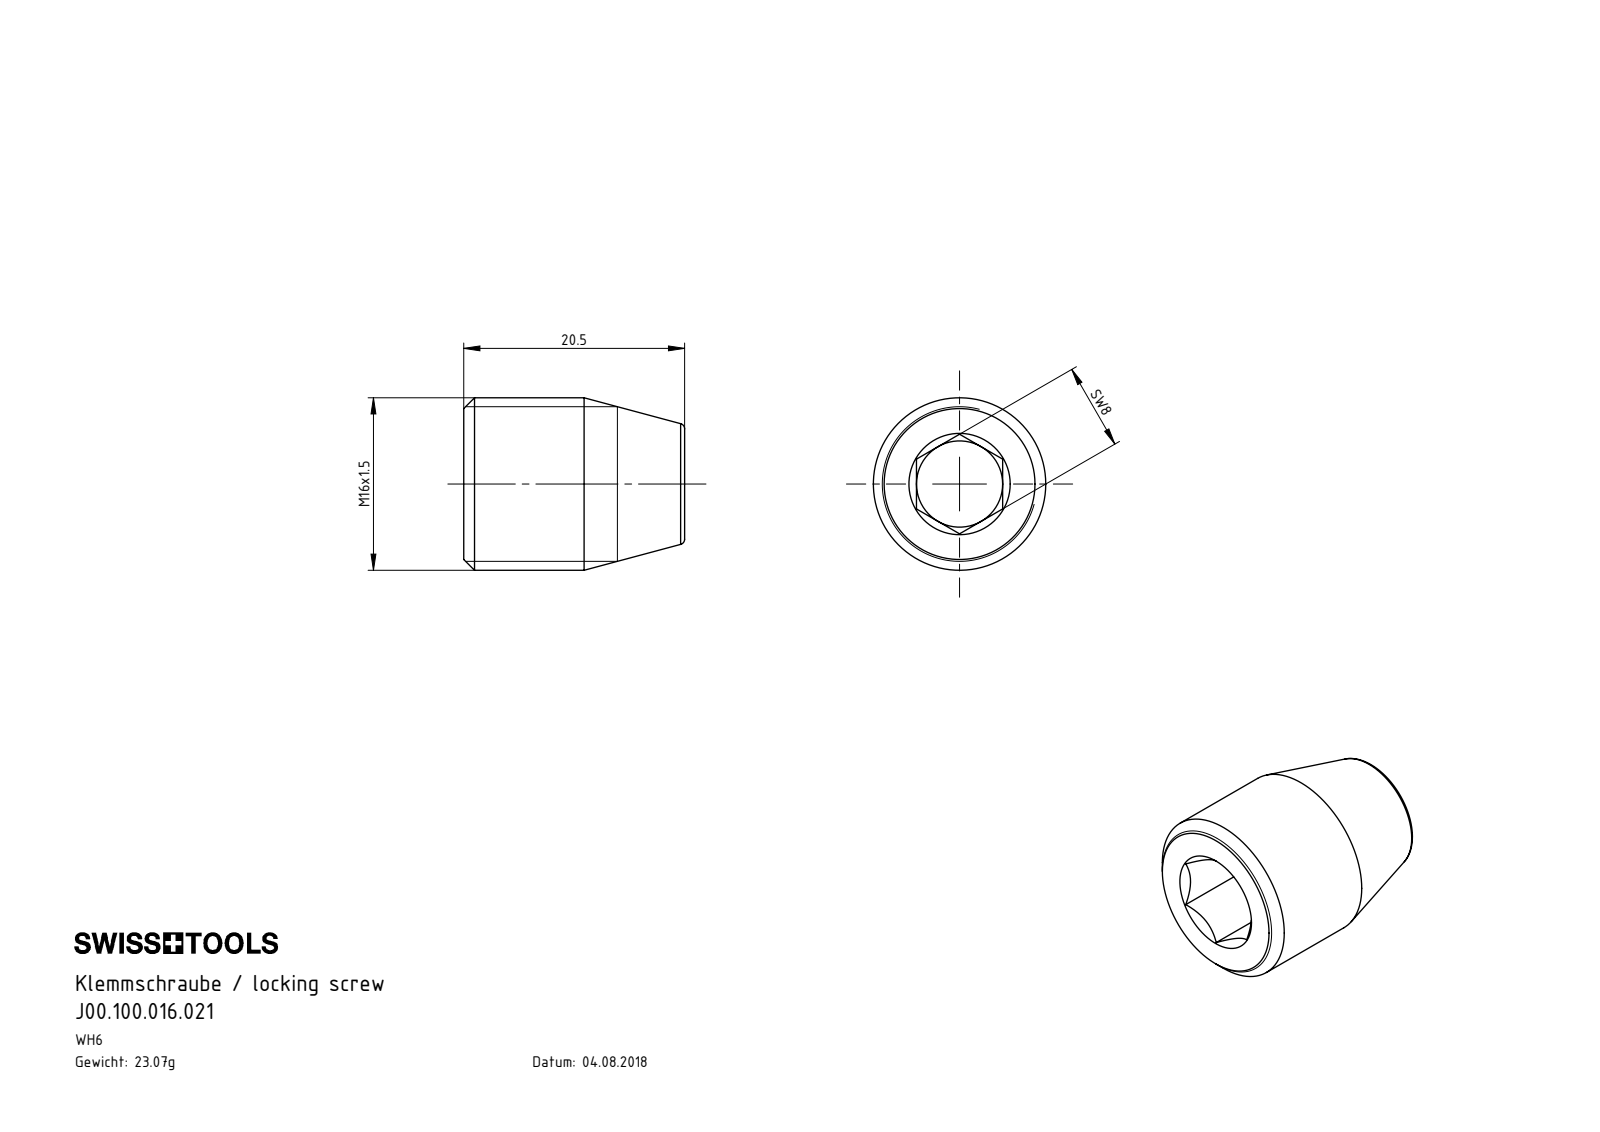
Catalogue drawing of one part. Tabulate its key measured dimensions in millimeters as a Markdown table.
| quantity | value |
| --- | --- |
| part name | J00.100.016.021 |
| STEP written by | SolidWorks 2017 (AUTOMOTIVE_DESIGN) |
| units | millimeters |
| bodies | 1 solid, 21 faces (14 planar, 2 cylindrical, 5 other) |
| overall size | 20.5 × 16 × 16 |
| volume | 2 939 mm³ |
| surface area | 1 530 mm² |
| round holes (diameter × count) | 8 × 1 |
| round bosses / shafts (diameter × count) | 16 × 1 |
| main face-to-face distances | 8, 20.5, 10, 10.5 |
